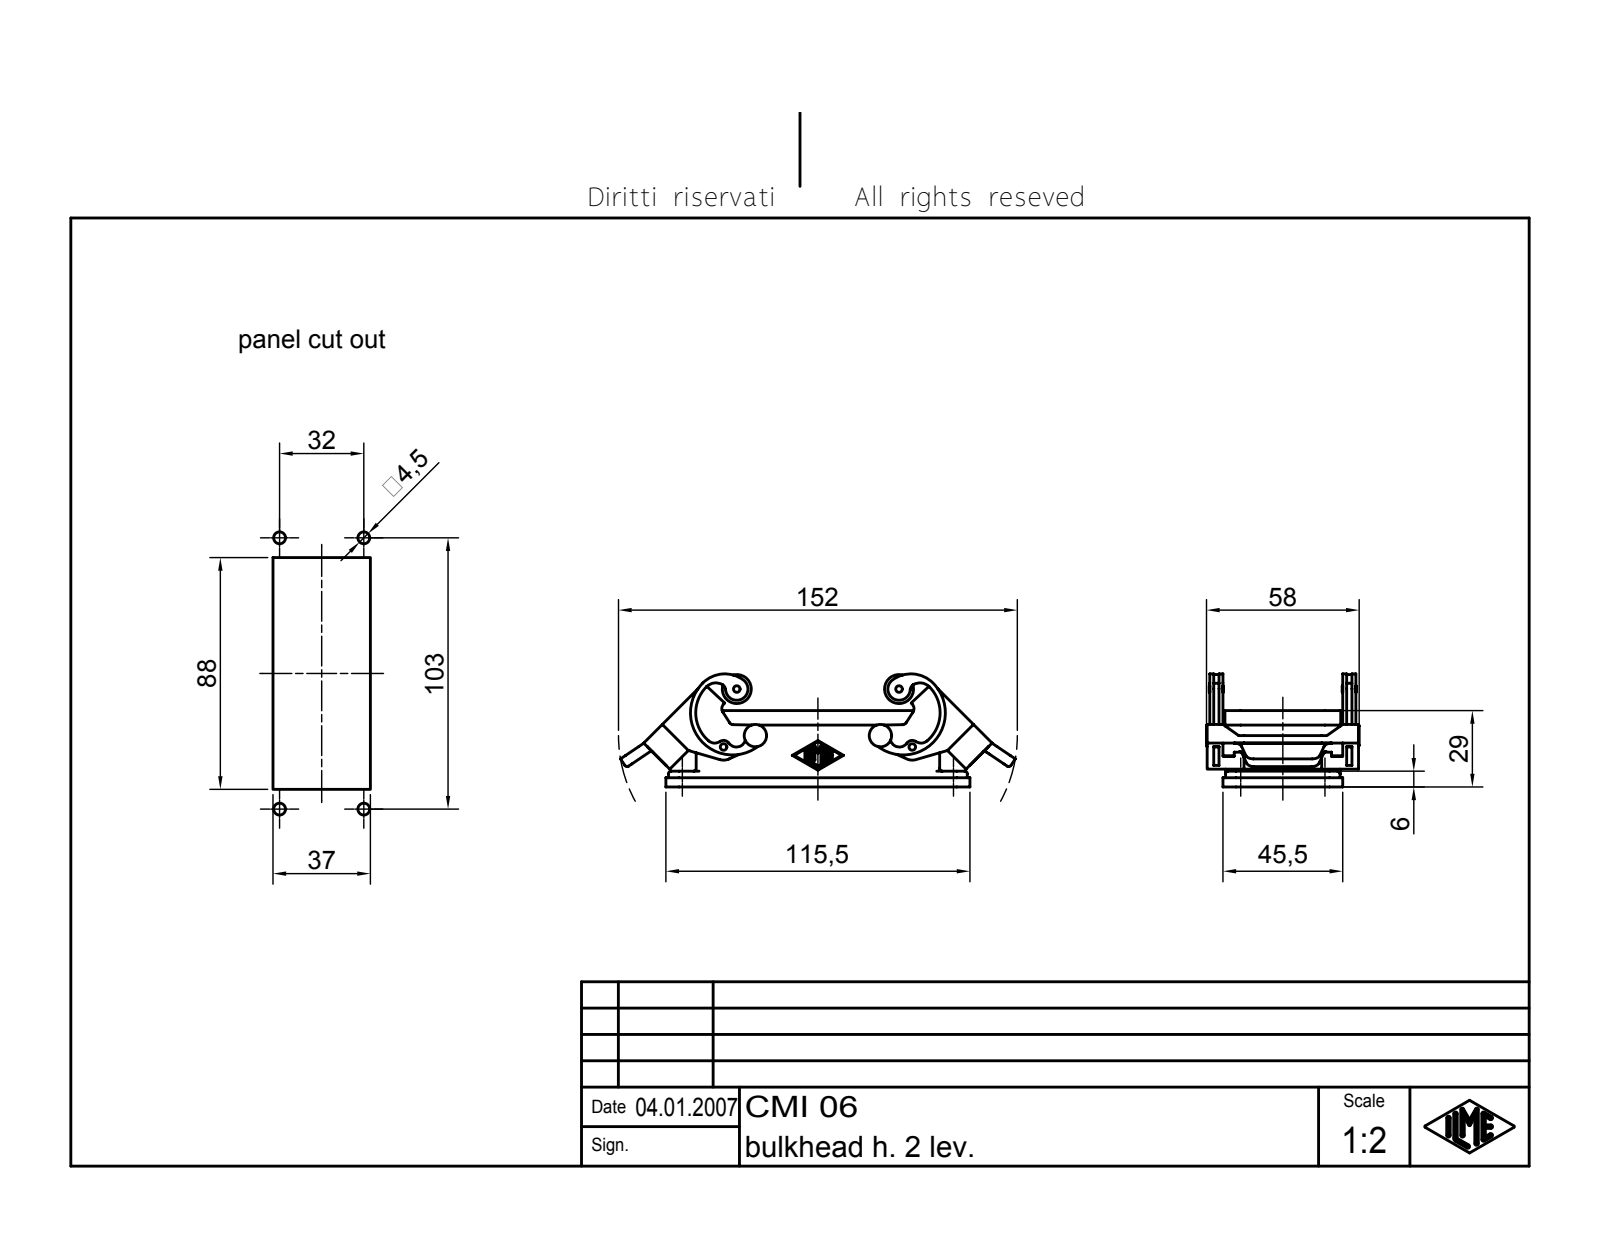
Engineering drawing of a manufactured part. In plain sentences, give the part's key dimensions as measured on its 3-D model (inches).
The part is named "CMI 06". Its 3-D file was written by "Autodesk Inventor 7 (AUTOMOTIVE_DESIGN)". It is 1 solid with 749 faces: 201 planar, 220 cylindrical and 328 other. Overall it measures 5.905 by 2.283 by 1.691 inches. Its volume is 3.239 cubic inches and its surface area 56.87 square inches. Round holes: 4 of diameter 0.079, 4 of diameter 0.177, 4 of diameter 0.181, 2 of diameter 0.098. Round bosses or shafts: 2 of diameter 0.433, 2 of diameter 0.197, 2 of diameter 0.118. Partial cylindrical surfaces (rounded edges, fillets, slot ends): 14 of radius 0.015, 14 of radius 0.039, 12 of radius 0.118, 10 of radius 0.098, 8 of radius 0.138, 8 of radius 0.197, 8 of radius 0.236, 6 of radius 0.157. The main face-to-face distances are 0.118, 0.157, 1.594, 0.039, 0.03, 0.138, 0.098, 1.604, 1.988, 0.167. The hole center spacings are 0.888, 1.26, 2.763, 4.055, 4.246, 2.427, 2.822.
